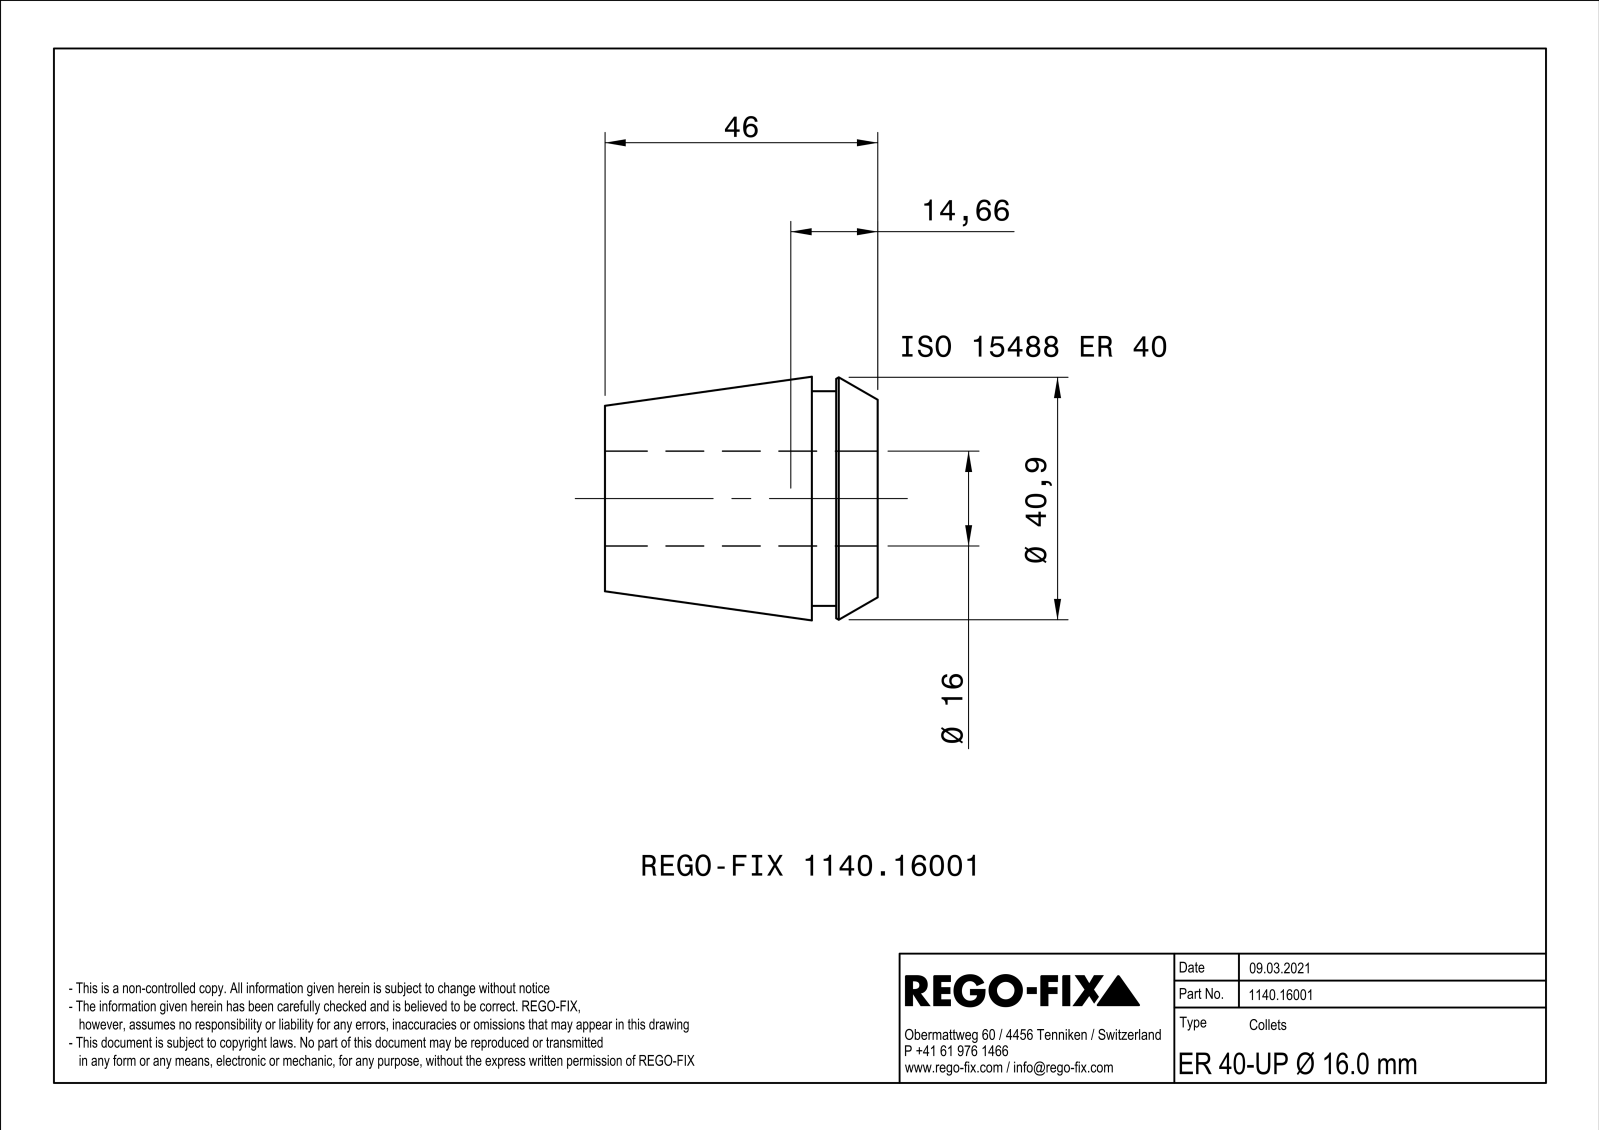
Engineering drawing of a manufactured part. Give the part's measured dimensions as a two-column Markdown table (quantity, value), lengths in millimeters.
| quantity | value |
| --- | --- |
| part name | NOCUT |
| STEP written by | SIEMENS PLM Software Solid Edge ST10 (AUTOMOTIVE_DESIGN) |
| units | millimeters |
| bodies | 1 solid, 177 faces (88 planar, 9 cylindrical, 80 other) |
| overall size | 46 × 40.99 × 40.99 |
| volume | 31 974 mm³ |
| surface area | 21 332 mm² |
| round holes (diameter × count) | 16 × 1 |
| round bosses / shafts (diameter × count) | 36.2 × 1 |
| main face-to-face distances | 1, 46, 11.1, 34.9, 7, 4.1, 39, 7.5, 0.5, 3.6 |
